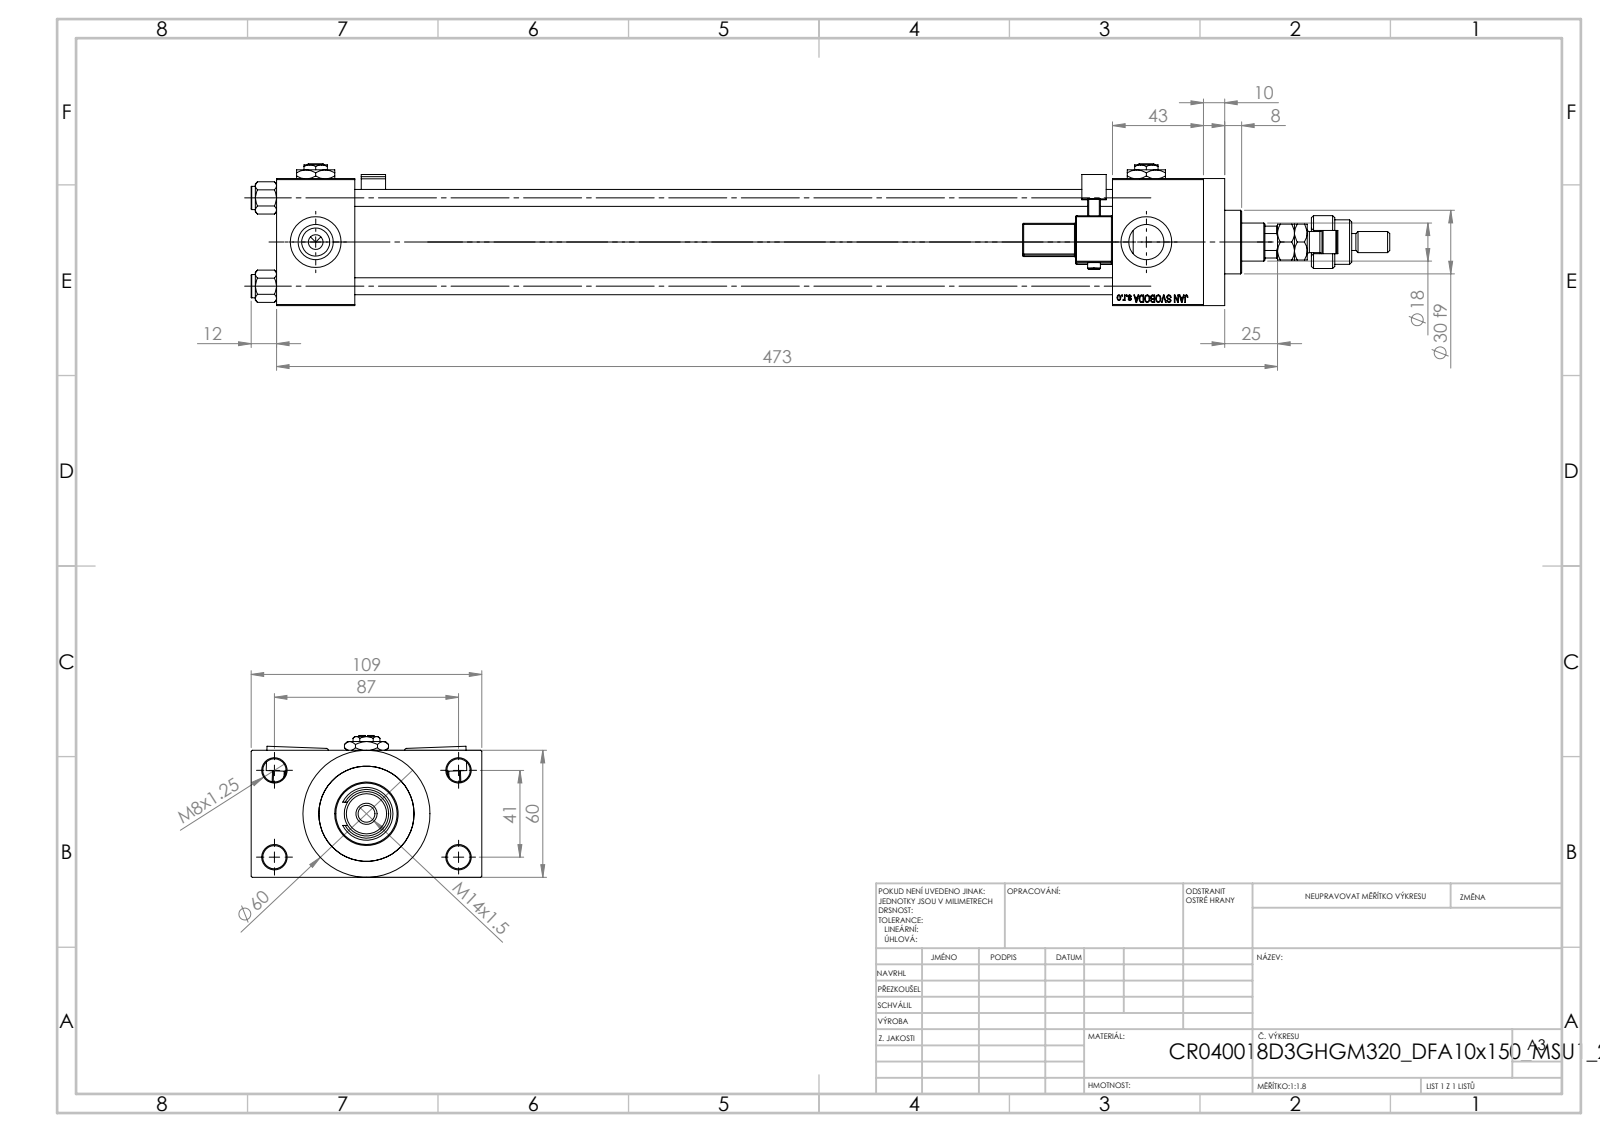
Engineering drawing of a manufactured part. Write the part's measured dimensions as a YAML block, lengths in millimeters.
part_name: "MFA; V215_VC_A; V215CR_VCP_D; V215CR_MSU (+5 more)"
step_written_by: "SolidWorks 2019 (CONFIG_CONTROL_DESIGN)"
units: millimeters
bodies: {solids: 17, faces: 1444, planar: 632, cylindrical: 172, other: 640}
overall_size: [538, 109, 67]
volume: 821206
surface_area: 270901
round_holes:
  - {diameter: 8, count: 4}
  - {diameter: 11, count: 4}
  - {diameter: 16.66, count: 4}
  - {diameter: 24, count: 4}
  - {diameter: 7, count: 3}
  - {diameter: 8.5, count: 1}
  - {diameter: 18, count: 1}
  - {diameter: 21, count: 1}
  - {diameter: 31, count: 1}
  - {diameter: 40, count: 1}
  - {diameter: 45, count: 1}
round_bosses_or_shafts:
  - {diameter: 11, count: 4}
  - {diameter: 6, count: 2}
  - {diameter: 60, count: 1}
  - {diameter: 46, count: 1}
  - {diameter: 30, count: 1}
  - {diameter: 25, count: 1}
  - {diameter: 16, count: 1}
  - {diameter: 10, count: 1}
partial_cylinders:
  - {radius: 0.5, count: 48}
  - {radius: 1, count: 2}
  - {radius: 2.5, count: 2}
  - {radius: 4, count: 2}
  - {radius: 5.5, count: 1}
  - {radius: 8.5, count: 1}
  - {radius: 8.75, count: 1}
face_to_face_distances: [60, 358, 24.5, 84.5, 37, 395, 43, 438, 401, 10]
hole_center_spacings: [22.65, 29.49, 41.7, 47.15, 48.09, 64.35, 76.49, 41]
